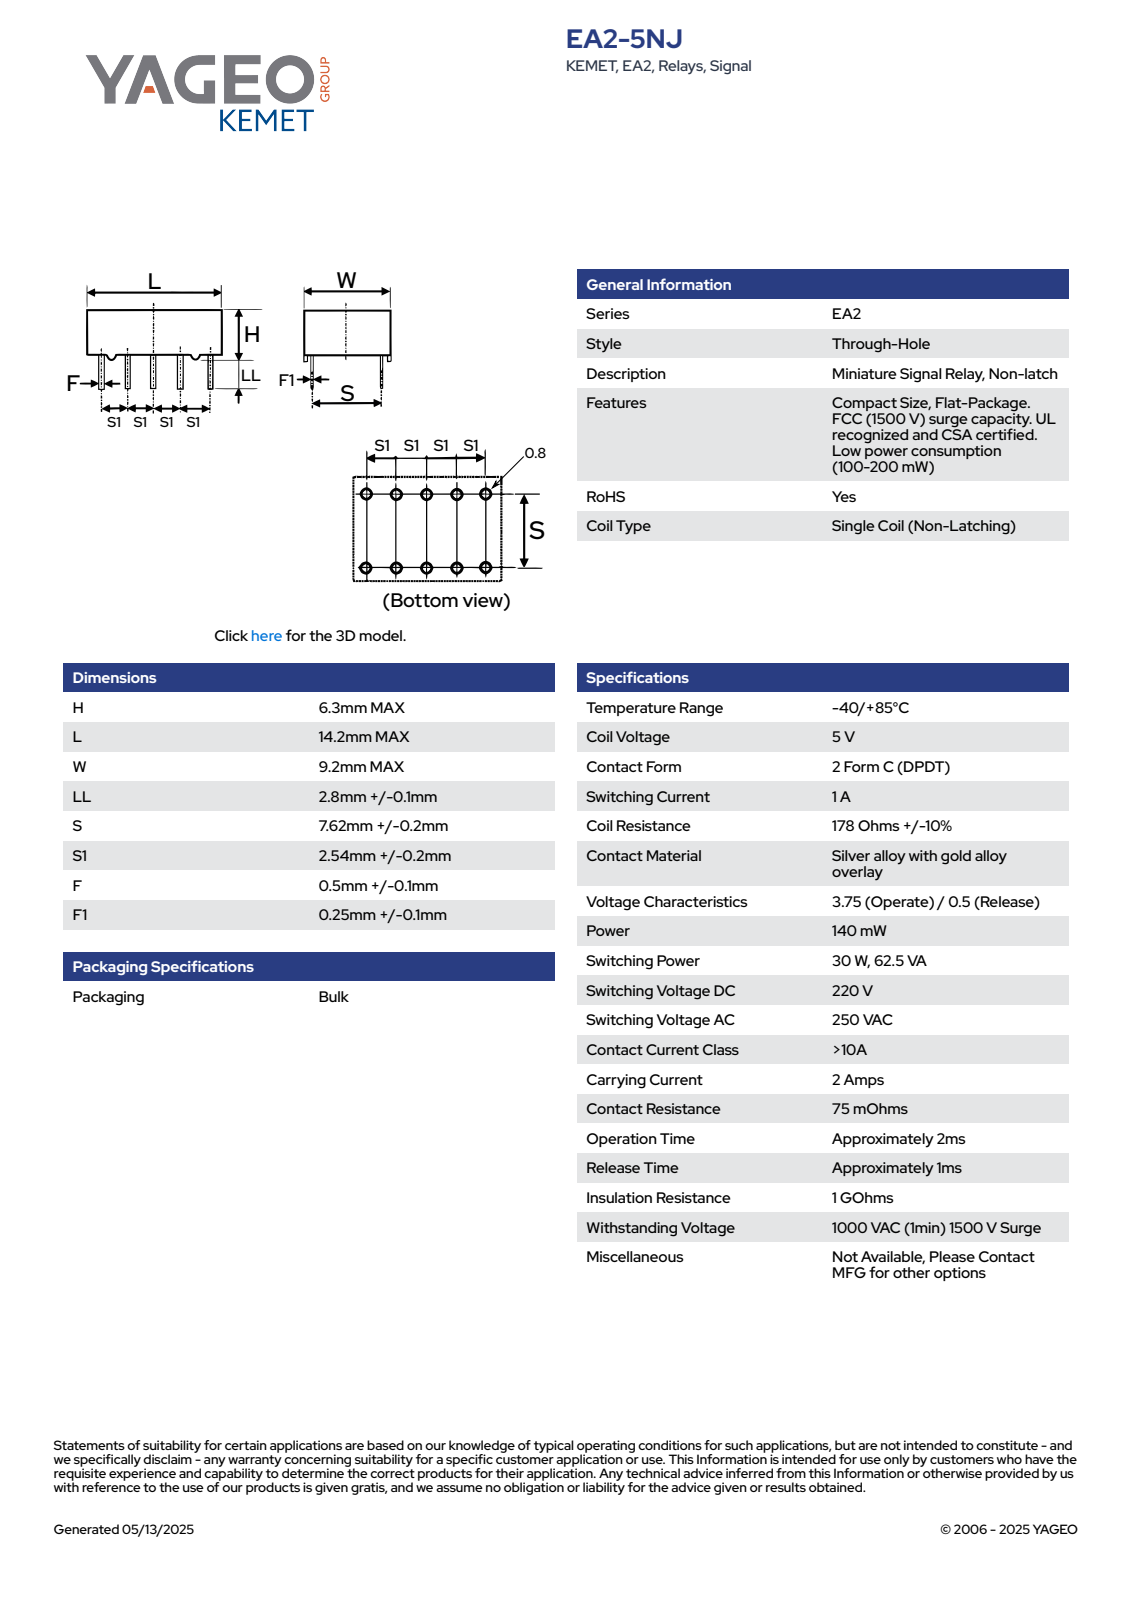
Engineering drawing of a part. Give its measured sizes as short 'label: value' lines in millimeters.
name: IR_TEA2_L14.2W9.2H6.3
written by: SolidWorks 2014 (AUTOMOTIVE_DESIGN)
unit: mm
bodies: 1 solid, 118 faces (114 planar, 4 cylindrical, 0 other)
size: 14.2 × 9.2 × 9.2
volume: 784 mm³; area: 603 mm²
rounds: 2× R0.35
face distances: 5.95, 9.2, 14.2, 7.62, 0.35, 2.54, 5.08, 0.61, 0.96, 8.24
